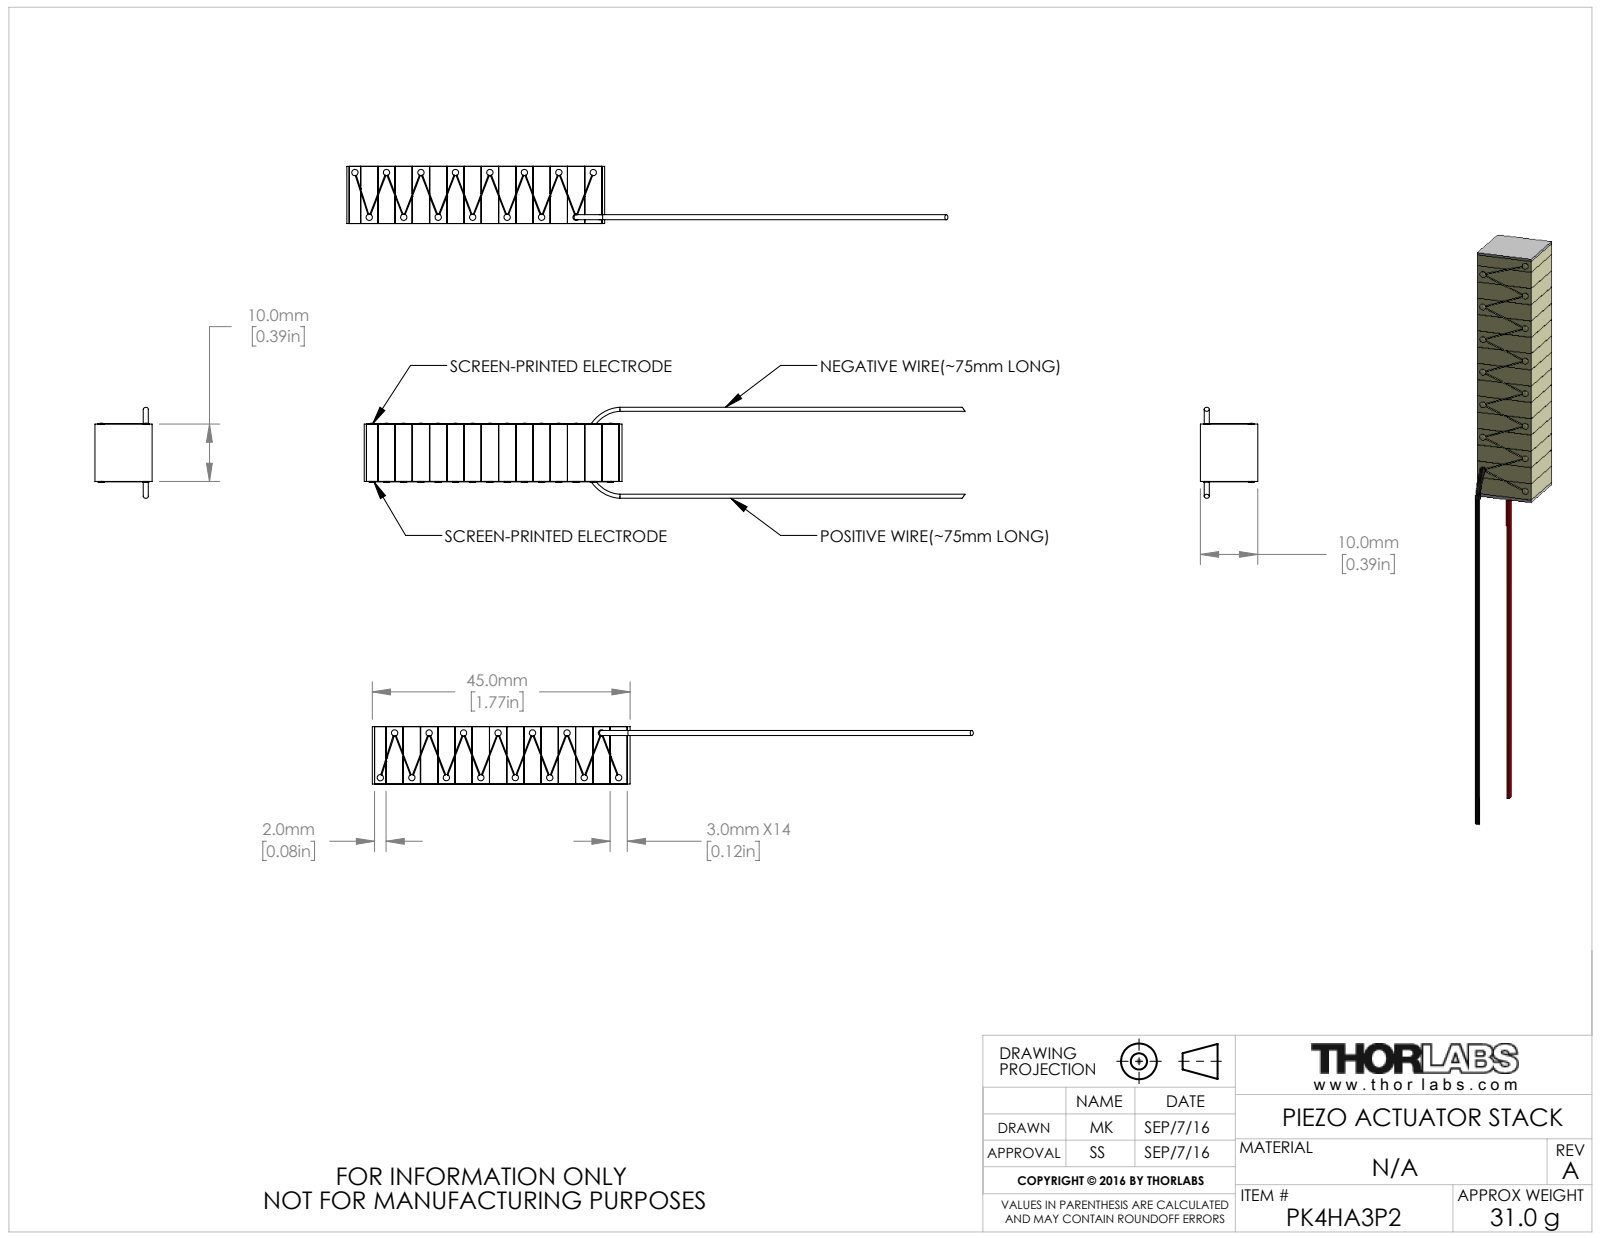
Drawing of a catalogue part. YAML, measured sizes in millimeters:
part_name: "CTN009397"
step_written_by: "SolidWorks 2016 (AUTOMOTIVE_DESIGN)"
units: millimeters
bodies: {solids: 4, faces: 494, planar: 280, cylindrical: 90, other: 124}
overall_size: [104.95, 15.89, 10]
volume: 8959
surface_area: 10356
round_bosses_or_shafts:
  - {diameter: 1.1, count: 15}
face_to_face_distances: [6.02, 3.01, 12.04, 6.01, 9.03, 10, 12.03, 3, 15.05, 18.06]
